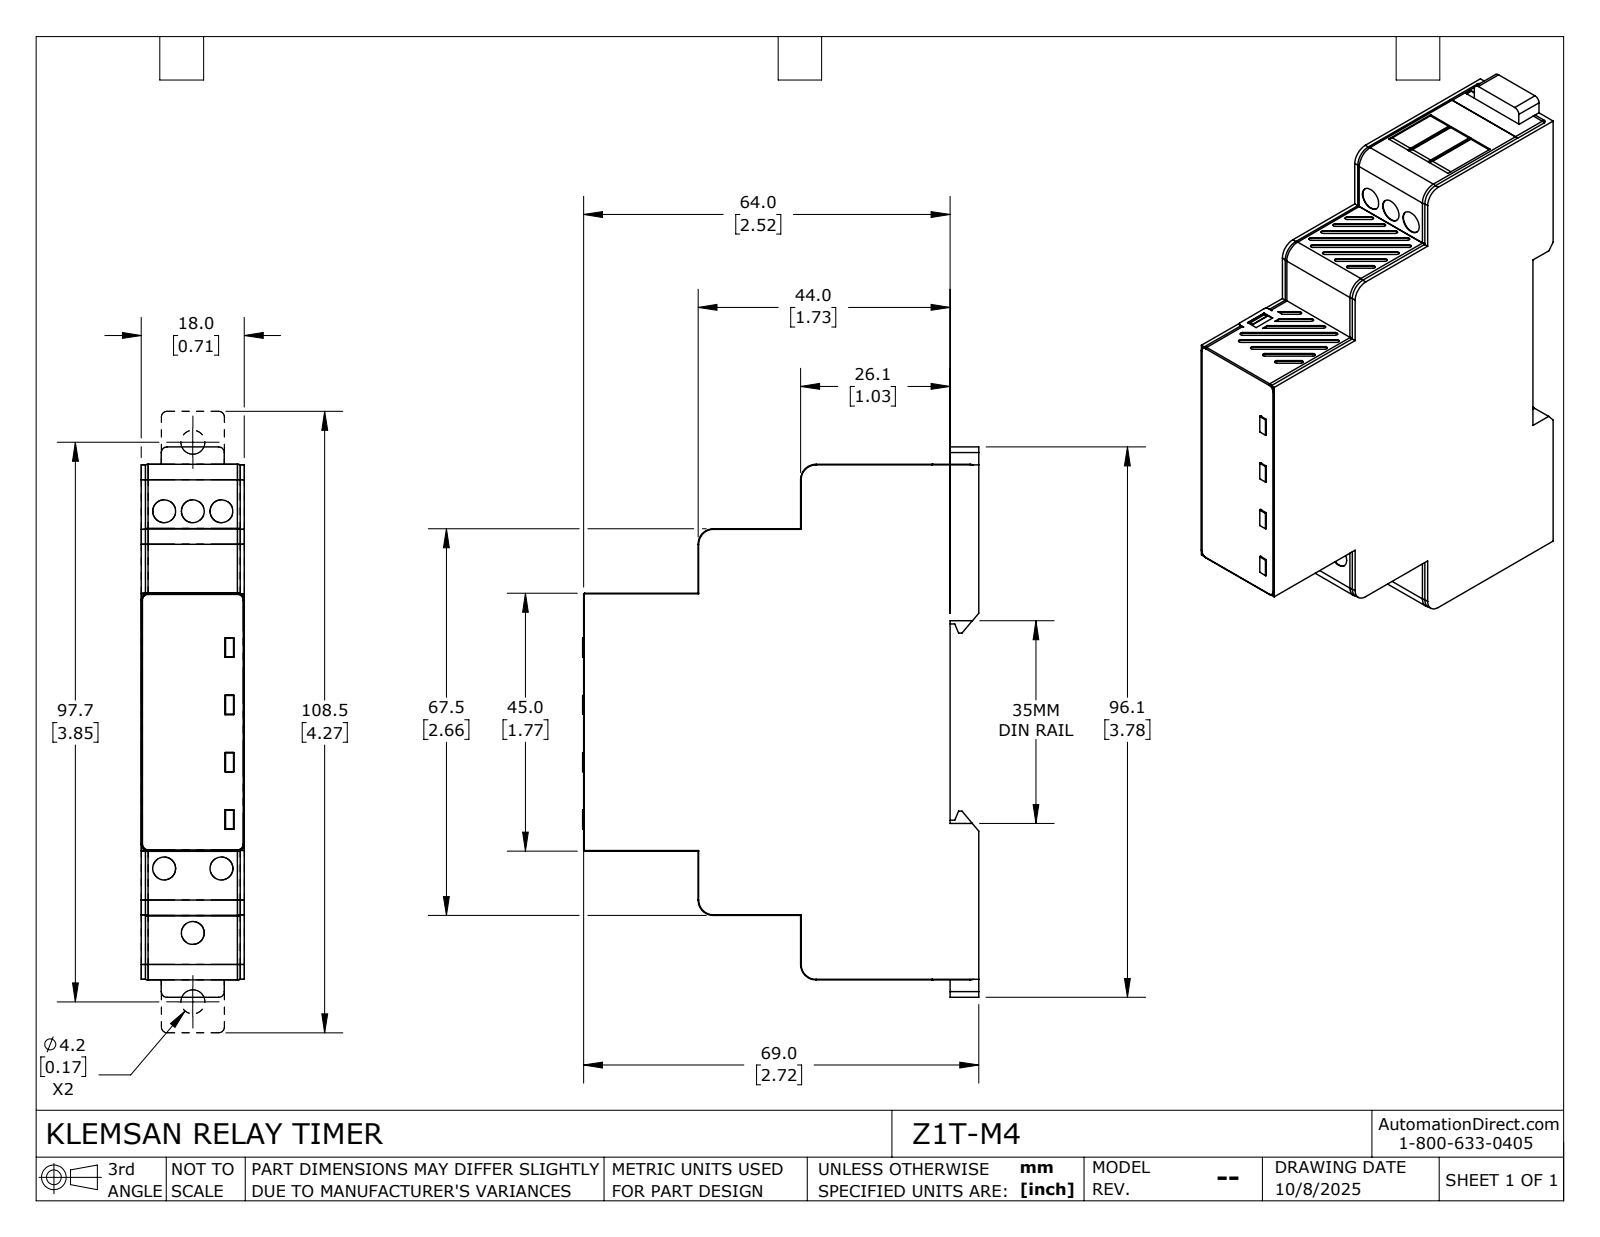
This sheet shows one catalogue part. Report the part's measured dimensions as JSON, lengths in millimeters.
{"part_name": "Z1T-M4", "step_written_by": "SolidWorks 2024 (CONFIG_CONTROL_DESIGN)", "units": "millimeters", "bodies": {"solids": 3, "faces": 440, "planar": 280, "cylindrical": 60, "other": 100}, "overall_size": [96.07, 69.15, 18], "volume_mm3": 83847, "surface_area_mm2": 17884, "round_holes": [[4.2, 2], [4, 1]], "partial_cylinders_radius": [[1.2, 16], [0.2, 4], [1, 4], [2.6, 4], [2.7, 4], [0.5, 2], [1.5, 2]], "face_to_face_distances": [18, 3.5, 14.5, 11.25, 64, 5, 69, 22.5, 67.4, 67.5], "hole_center_spacings": [5.83, 79.43, 85.26]}
